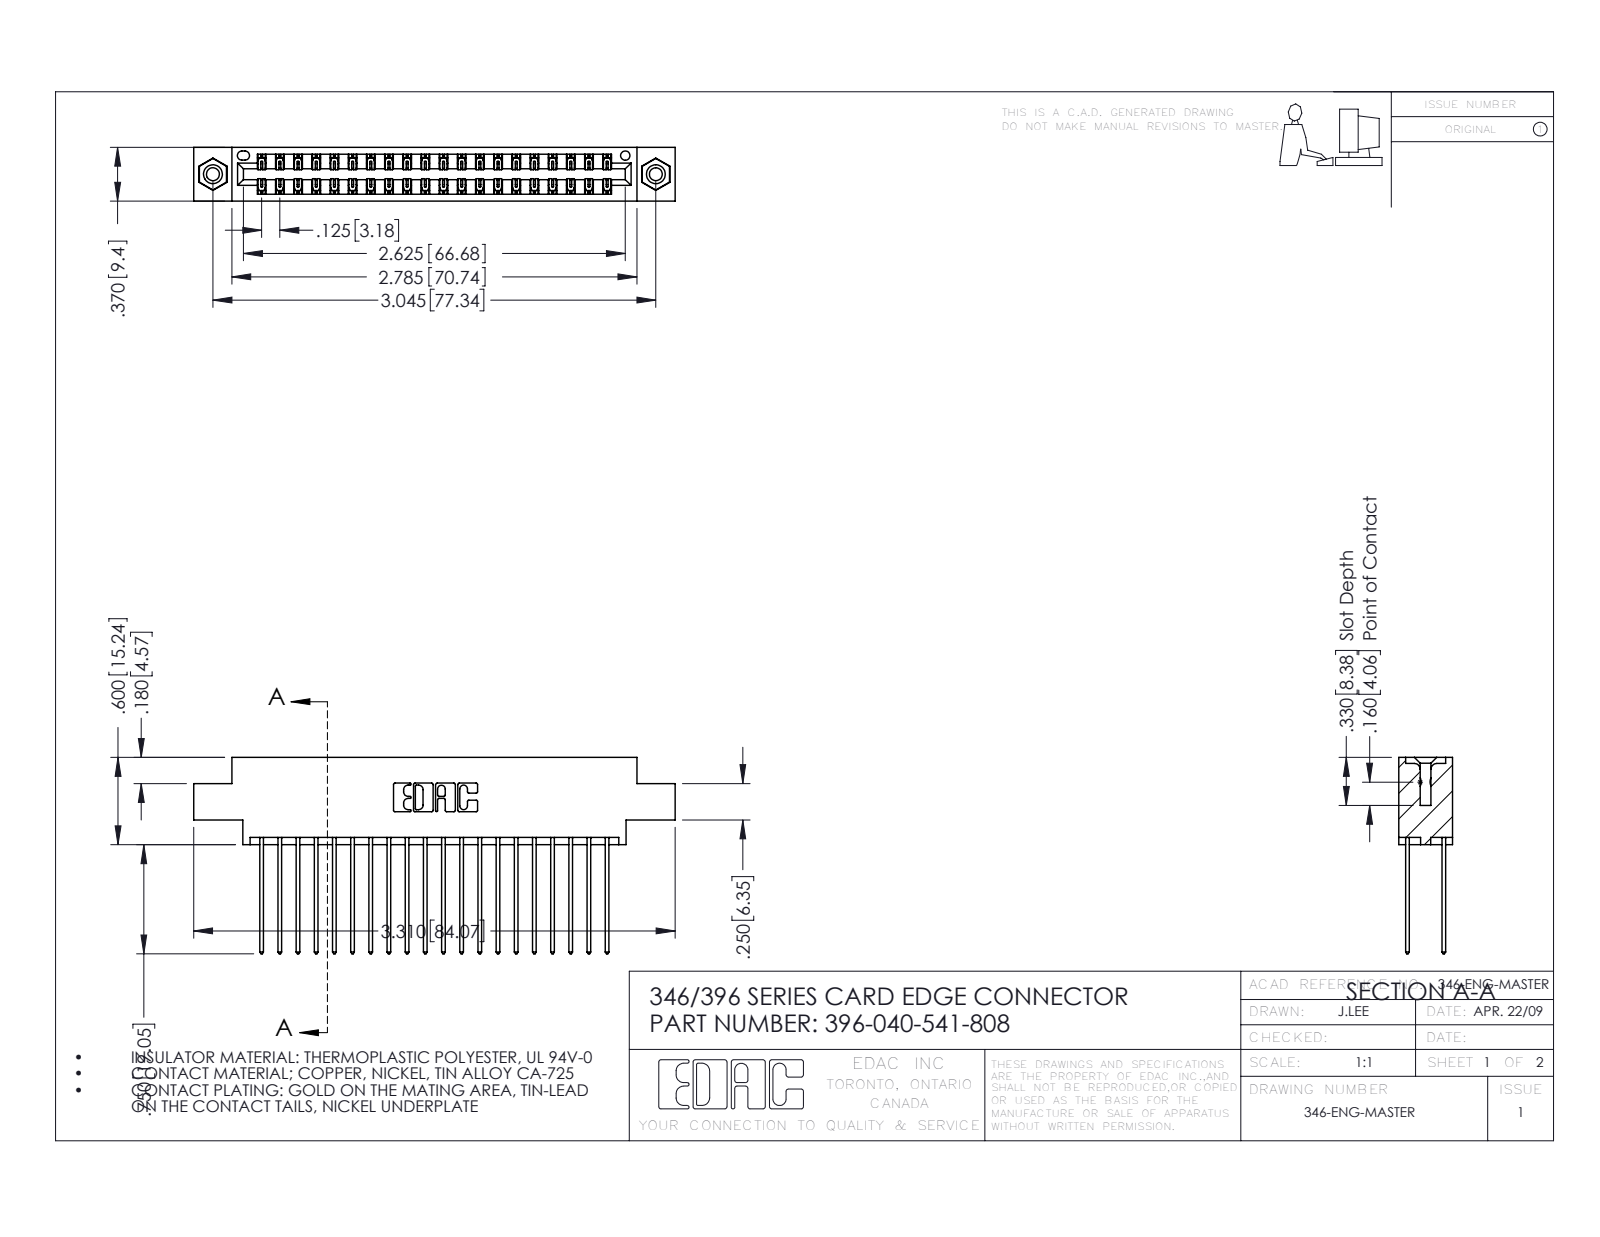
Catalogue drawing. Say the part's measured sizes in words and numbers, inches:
The part is named "345-250-001_345-250-003-102; 396-040-541-808; 345-292-001_345-293-141; 346 Part_0.170 Offset - 0.156 Dia-TI". Its 3-D file was written by "SolidWorks 2016 (CONFIG_CONTROL_DESIGN)". It is 43 solids with 2266 faces: 1512 planar, 738 cylindrical and 16 other. Overall it measures 3.31 by 1.35 by 0.37 inches. Its volume is 0.494 cubic inches and its surface area 18.73 square inches. Round holes: 2 of diameter 0.089, 2 of diameter 0.125, 2 of diameter 0.156, 1 of diameter 0.064. Round bosses or shafts: 2 of diameter 0.155. Partial cylindrical surfaces (rounded edges, fillets, slot ends): 60 of radius 0.006, 40 of radius 0.01, 22 of radius 0.01, 6 of radius 0.007, 6 of radius 0.031, 3 of radius 0.026, 2 of radius 0.014, 2 of radius 0.022. The main face-to-face distances are 0.048, 0.322, 0.25, 0.072, 0.298, 0.025, 0.37, 0.275, 0.222, 0.225. The hole center spacings are 0.246, 2.837, 3.045.
